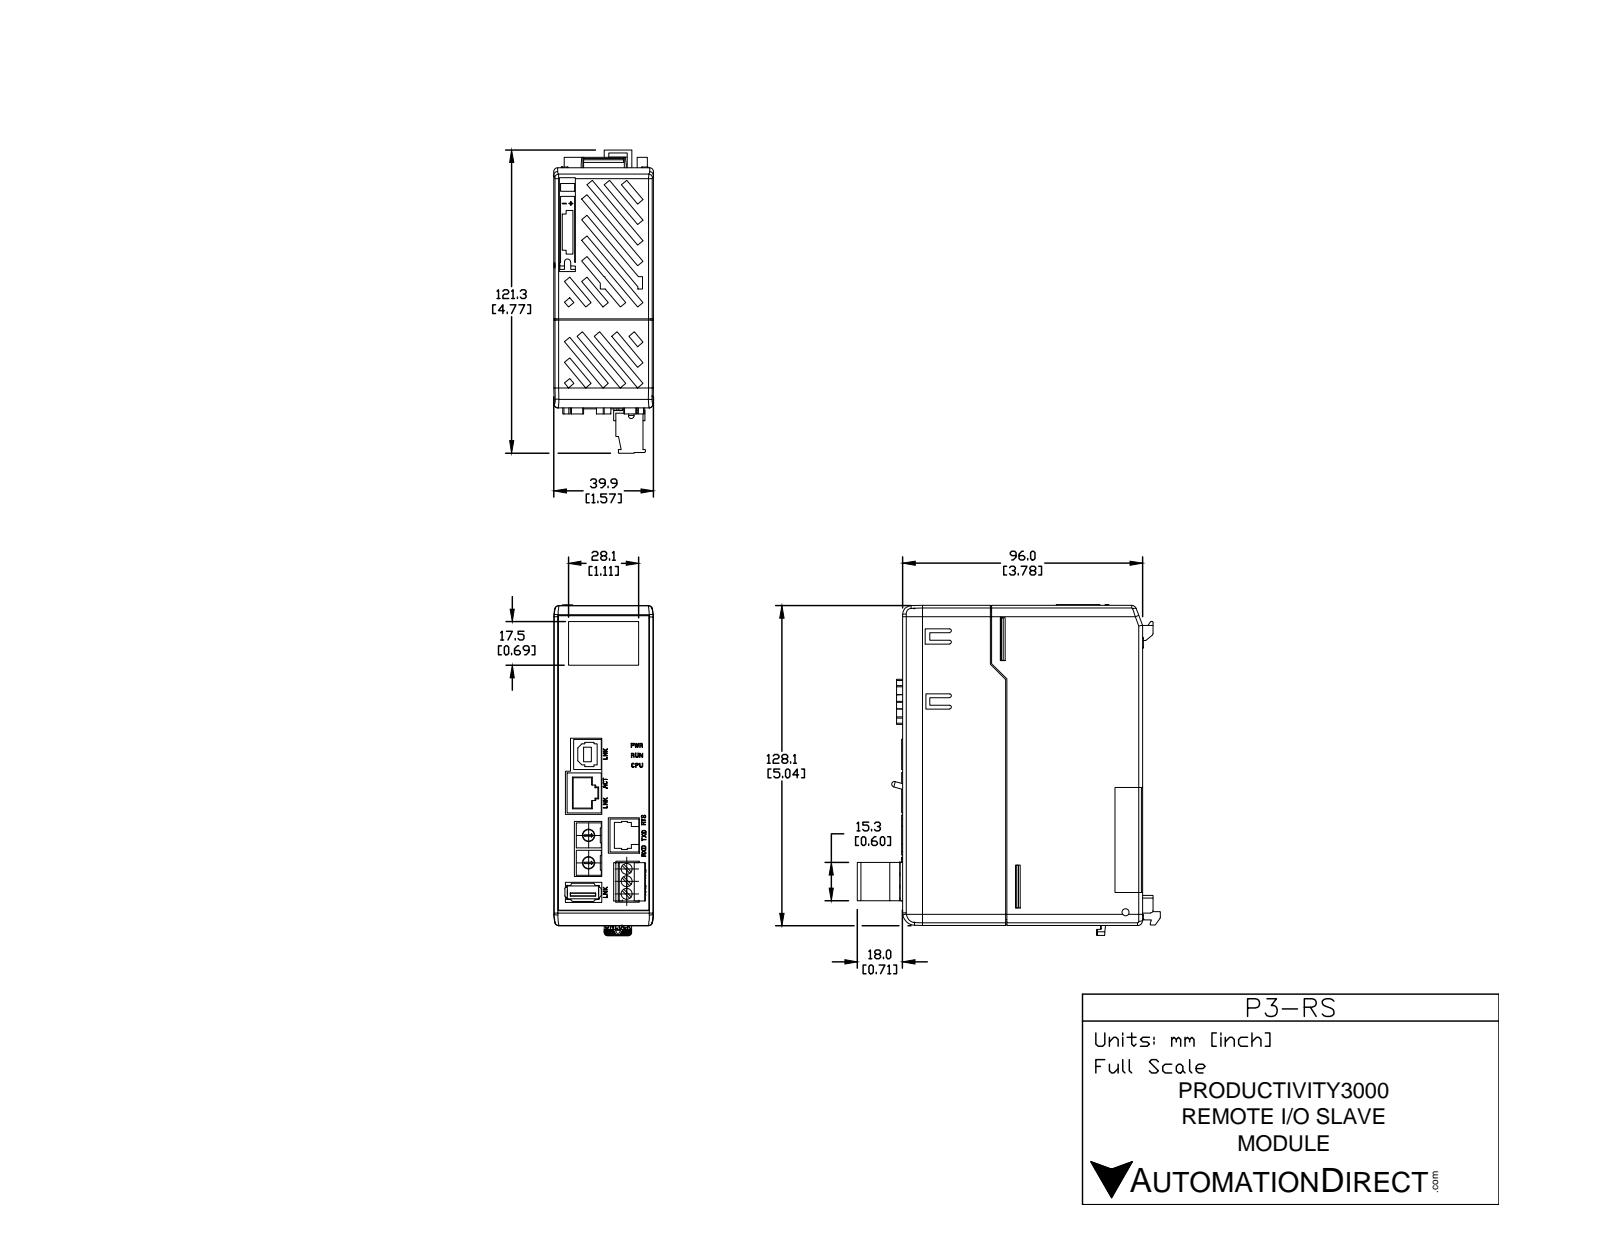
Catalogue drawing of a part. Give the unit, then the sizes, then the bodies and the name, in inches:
Units: inches
Overall size (bounding box): 5.212 × 4.775 × 1.571
Round holes (diameter × count): ⌀0.055 ×3, ⌀0.173 ×3, ⌀0.197 ×2, ⌀0.087 ×1, ⌀0.11 ×1
Round bosses / shafts (diameter × count): ⌀0.118 ×3, ⌀0.181 ×2
Partial cylindrical surfaces — rounded edges, fillets, slot ends (radius × count): R0.012 ×20, R0.059 ×14, R0.039 ×10, R0.138 ×7, R0.024 ×6, R0.02 ×5, R0.472 ×5, R0.004 ×4
Main face-to-face distances: 1.571, 0.02, 3.773, 5.023, 5.043, 5.003, 3.753, 3.761, 1.551, 3.741
Hole centre spacings: 0.197, 0.02, 0.196, 0.2, 0.394, 0.392, 0.396, 0.433
Volume: 29.88 in³ · Surface area: 72.76 in²
Bodies: 1 solid, 2005 faces (1806 planar, 156 cylindrical, 43 other)
Part name (STEP PRODUCT): P3-RS
STEP written by: SolidWorks 2009 (CONFIG_CONTROL_DESIGN)
